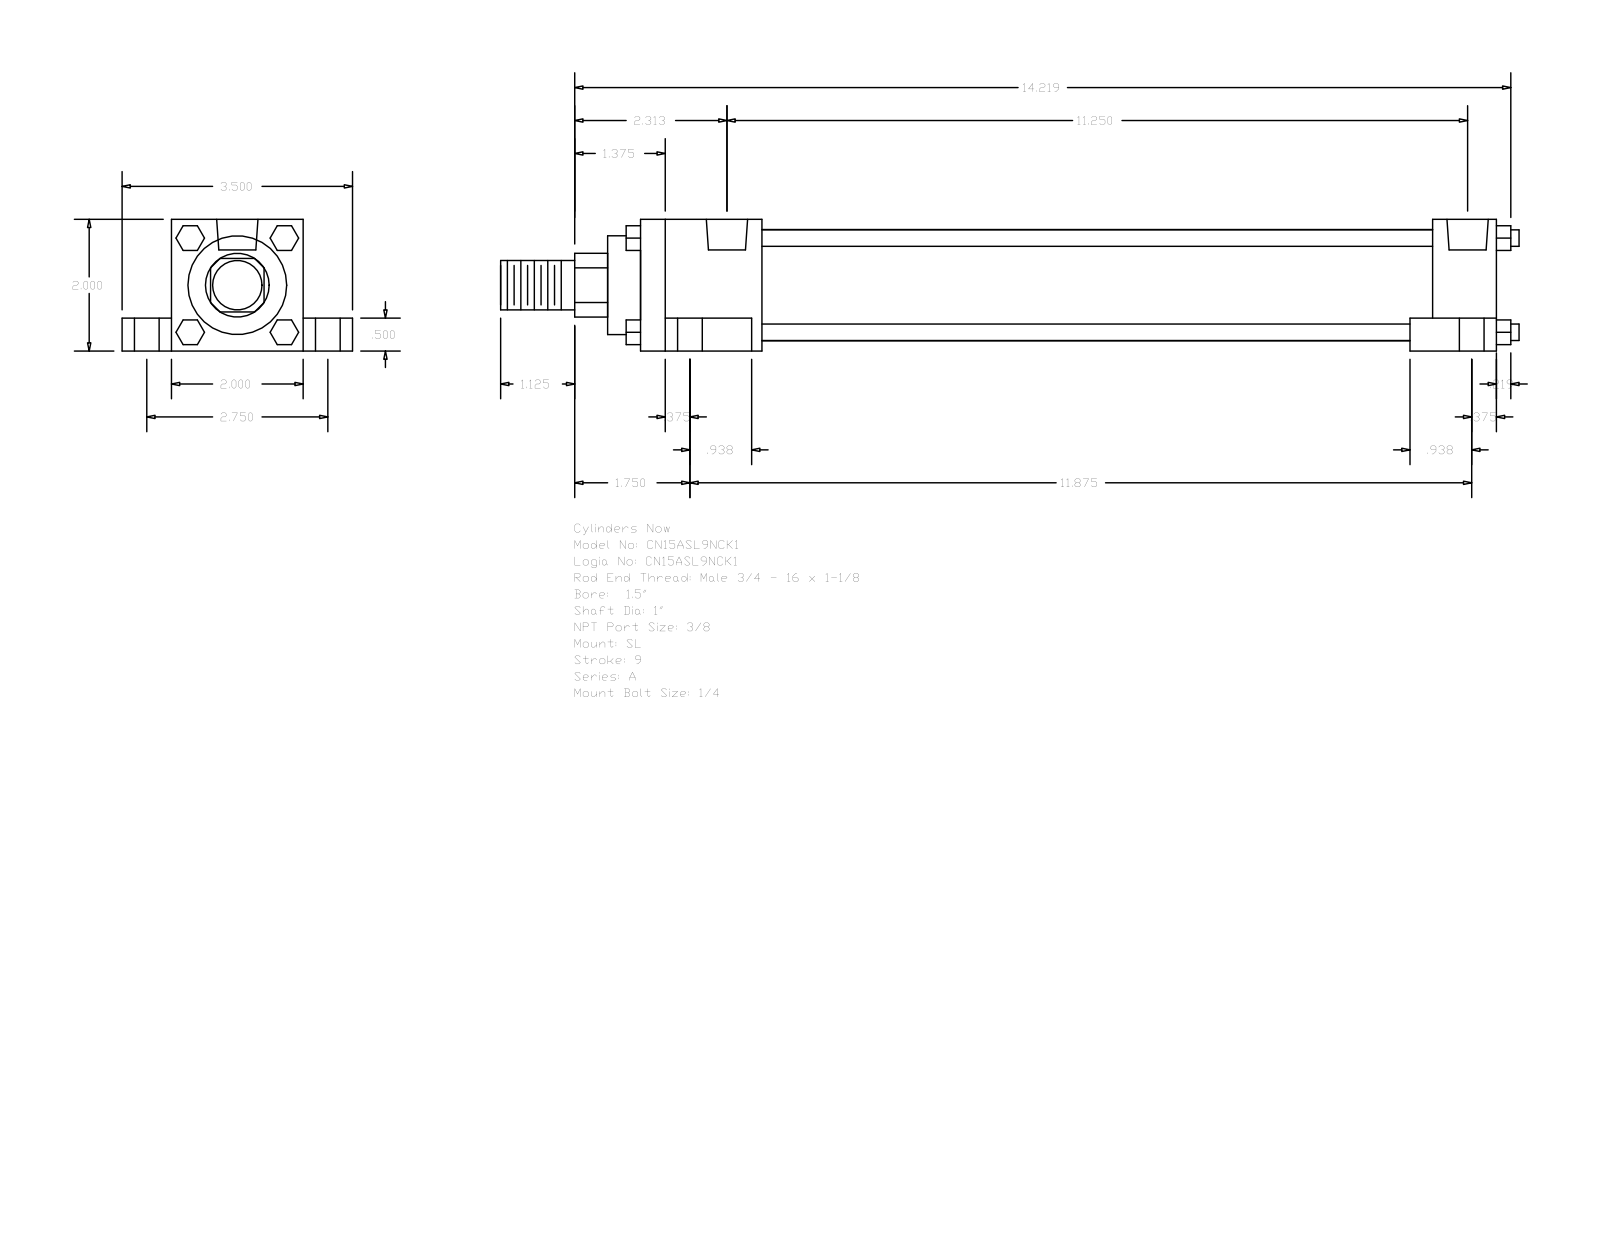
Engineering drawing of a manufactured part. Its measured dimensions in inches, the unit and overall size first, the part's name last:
Units: inches
Overall size (bounding box): 15.469 × 3.5 × 2
Round holes (diameter × count): ⌀0.219 ×4, ⌀0.375 ×4, ⌀0.625 ×4, ⌀0.627 ×2
Round bosses / shafts (diameter × count): ⌀0.25 ×4, ⌀1.69 ×1, ⌀1.5 ×1, ⌀1 ×1, ⌀0.75 ×1
Partial cylindrical surfaces — rounded edges, fillets, slot ends (radius × count): R0.484 ×1
Main face-to-face distances: 2, 0.5, 1.5, 0.75, 2.75, 0.375, 13, 1.313, 12.031, 0.969
Hole centre spacings: 0.156, 1.376, 1.392, 1.485, 1.552, 2.75, 10.937, 11.094
Bodies: 0 solids, 148 faces (112 planar, 36 cylindrical, 0 other)
Part name (STEP PRODUCT): A_SL__0150_1
STEP written by: GSSL Pune (CONFIG_CONTROL_DESIGN)
